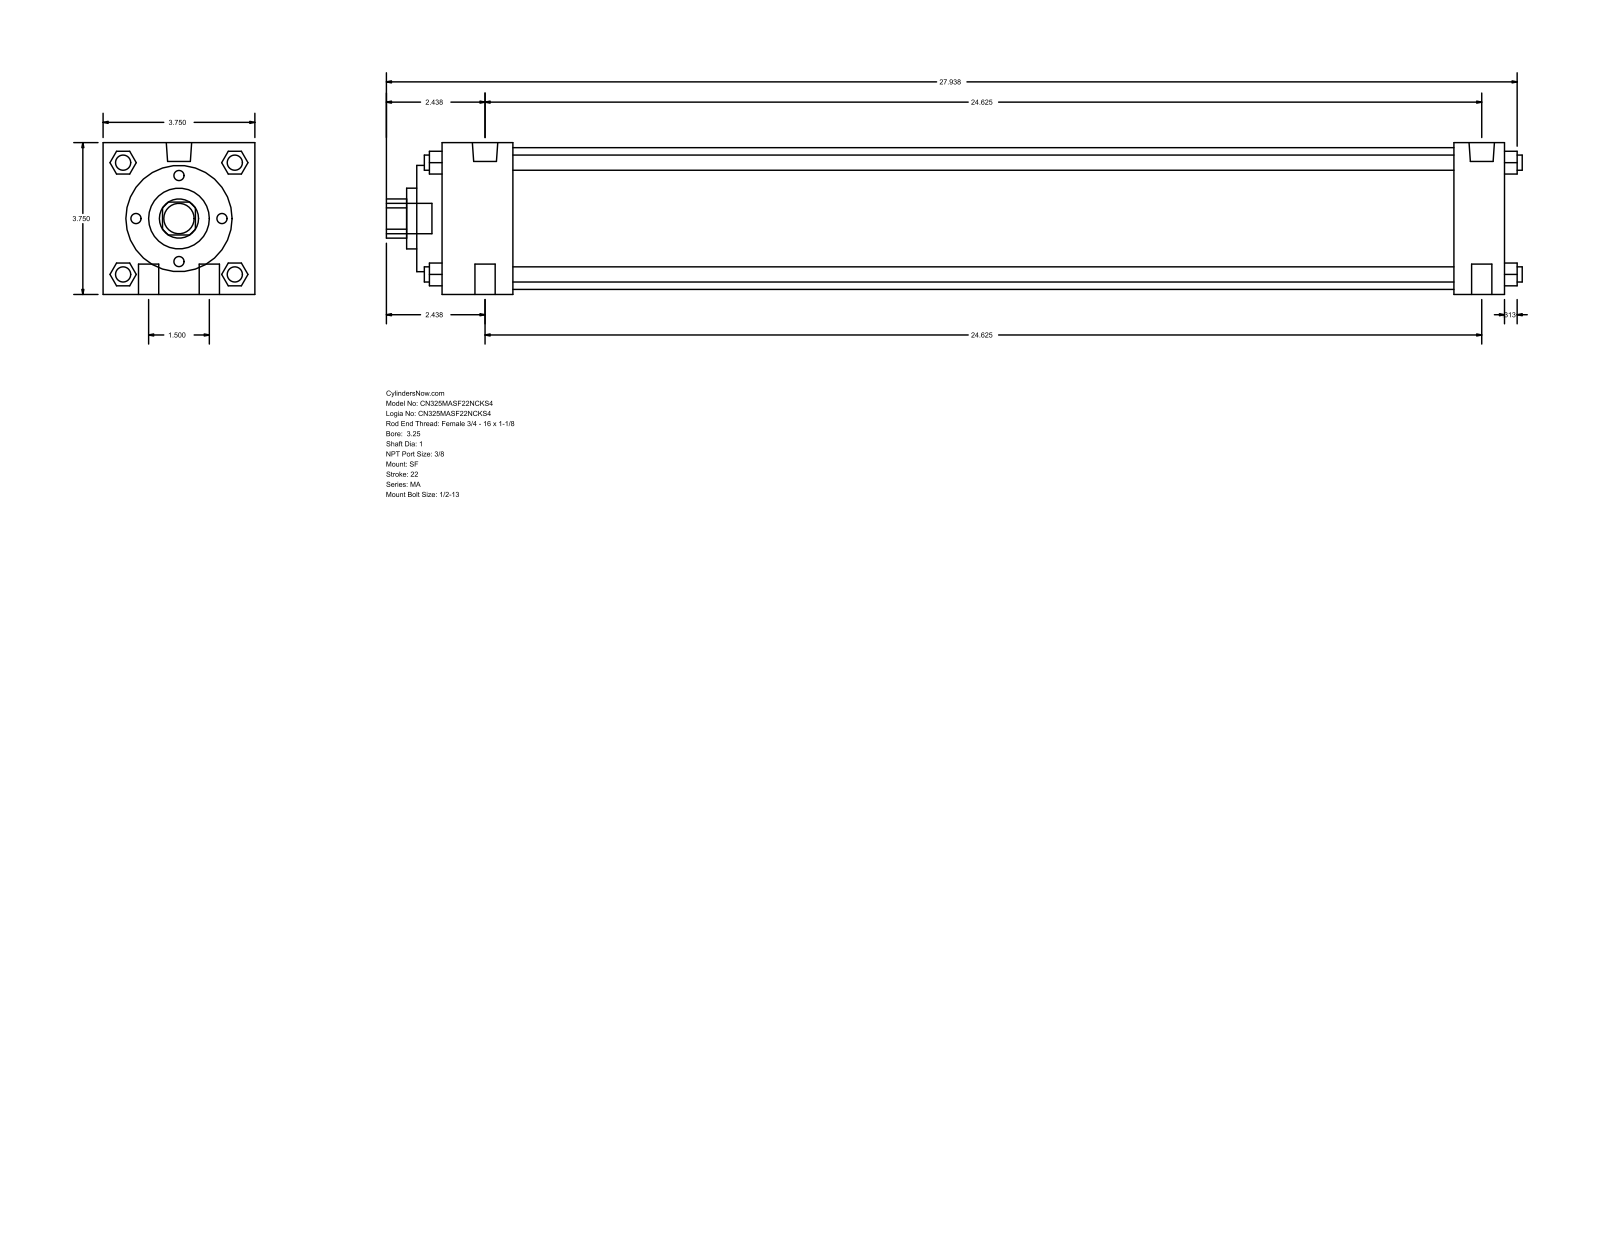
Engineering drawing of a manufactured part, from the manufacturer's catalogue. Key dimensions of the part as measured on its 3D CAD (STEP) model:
Part name (STEP PRODUCT): MA_SF__0325_1
STEP written by: GSSL Pune (CONFIG_CONTROL_DESIGN)
Units: millimetres
Bodies: 0 solids, 126 faces (95 planar, 31 cylindrical, 0 other)
Overall size (bounding box): 712.79 × 95.25 × 95.25
Round holes (diameter × count): ⌀25.4 ×1, ⌀38.1 ×1, ⌀66.67 ×1, ⌀88.9 ×1
Round bosses / shafts (diameter × count): ⌀12.7 ×4, ⌀9.53 ×4, ⌀15.93 ×2, ⌀11.11 ×2, ⌀19.05 ×1
Partial cylindrical surfaces — rounded edges, fillets, slot ends (radius × count): R12.29 ×1
Main face-to-face distances: 95.24, 666.75, 682.62, 15.87, 635, 31.75, 44.46, 590.54, 622.29, 60.33
